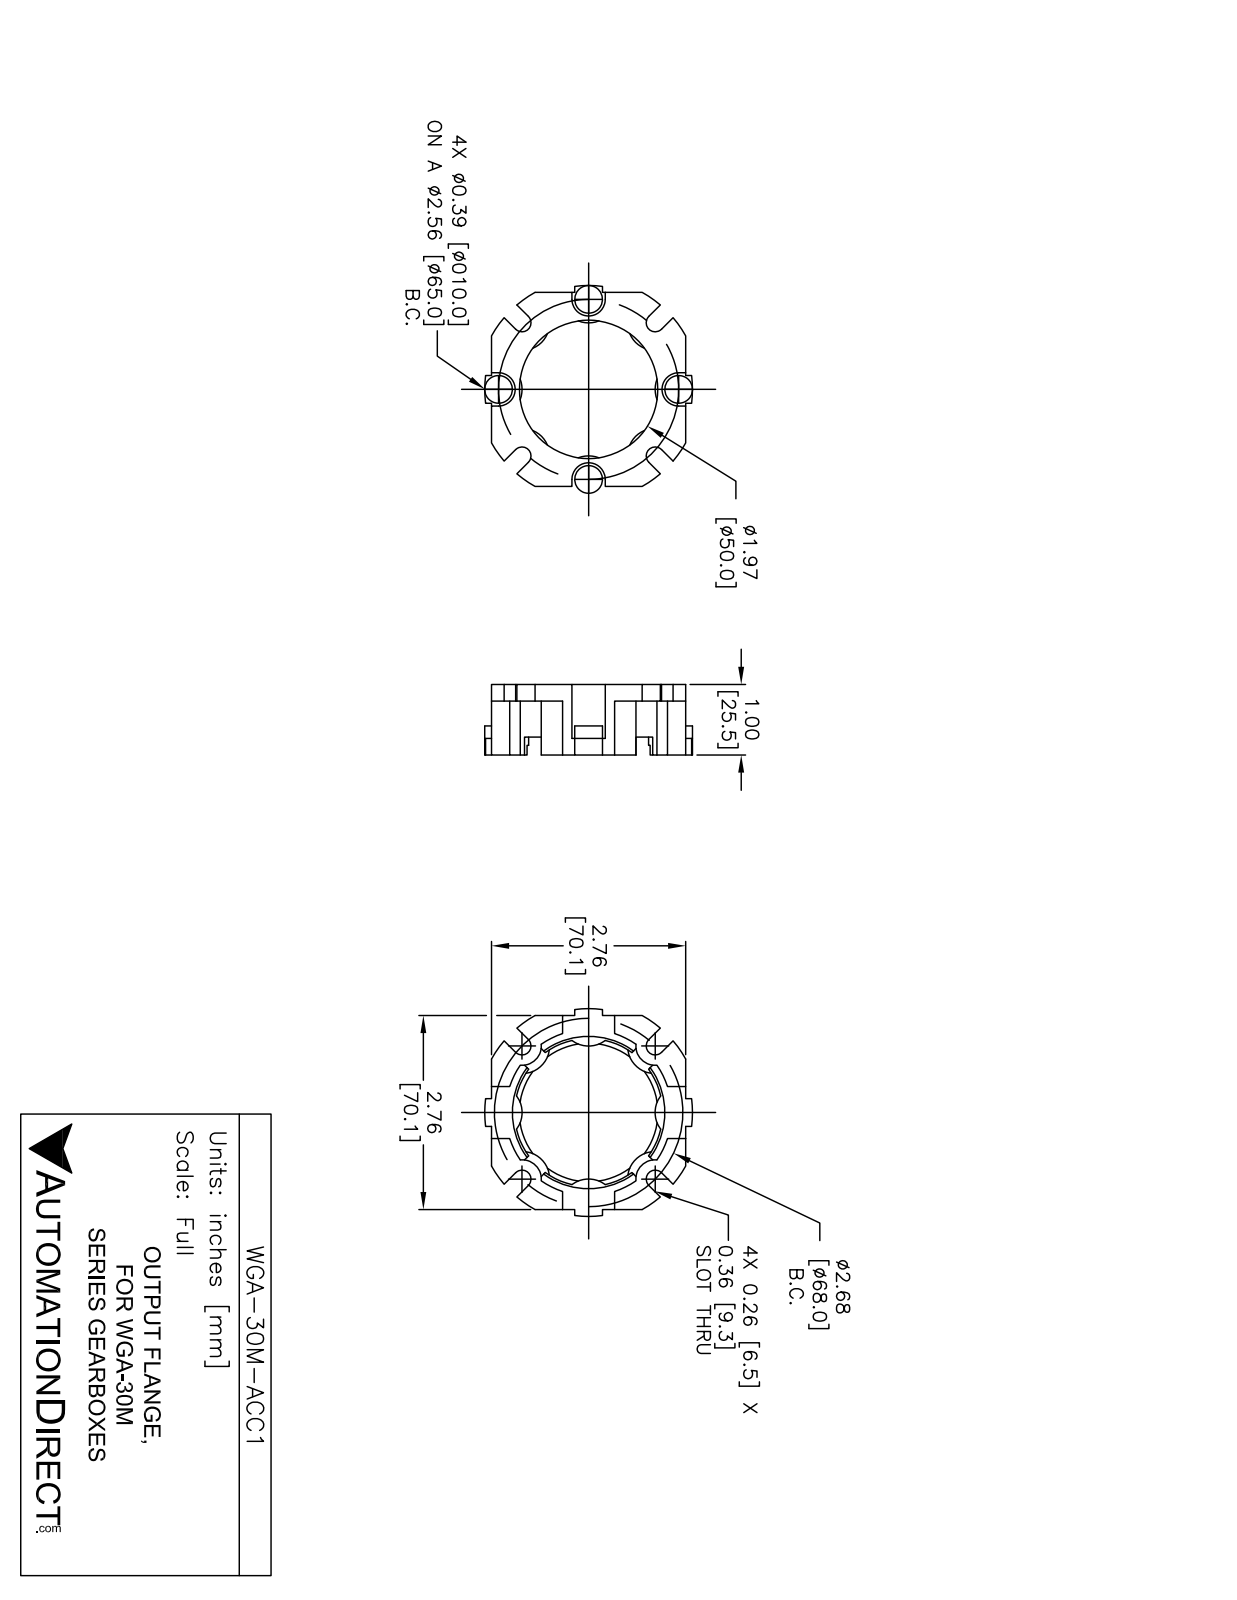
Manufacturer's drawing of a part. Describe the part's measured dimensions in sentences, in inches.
The part is named "WGA-30M-ACC1". Its 3-D file was written by "SolidWorks 2014 (AUTOMOTIVE_DESIGN)". It is 1 solid with 159 faces: 89 planar, 70 cylindrical and 0 other. Overall it measures 2.953 by 2.953 by 1.004 inches. Its volume is 1.78 cubic inches and its surface area 26.45 square inches. Round holes: 1 of diameter 1.969, 1 of diameter 2.165. Round bosses or shafts: 4 of diameter 0.394. Partial cylindrical surfaces (rounded edges, fillets, slot ends): 8 of radius 0.394, 4 of radius 0.128, 4 of radius 0.236, 4 of radius 0.276, 1 of radius 1.051, 1 of radius 1.181, 1 of radius 1.476, 1 of radius 1.575. The main face-to-face distances are 0.236, 1.749, 1.009, 0.768, 1.004, 2.758, 0.74, 0.433, 0.256, 1.143.
